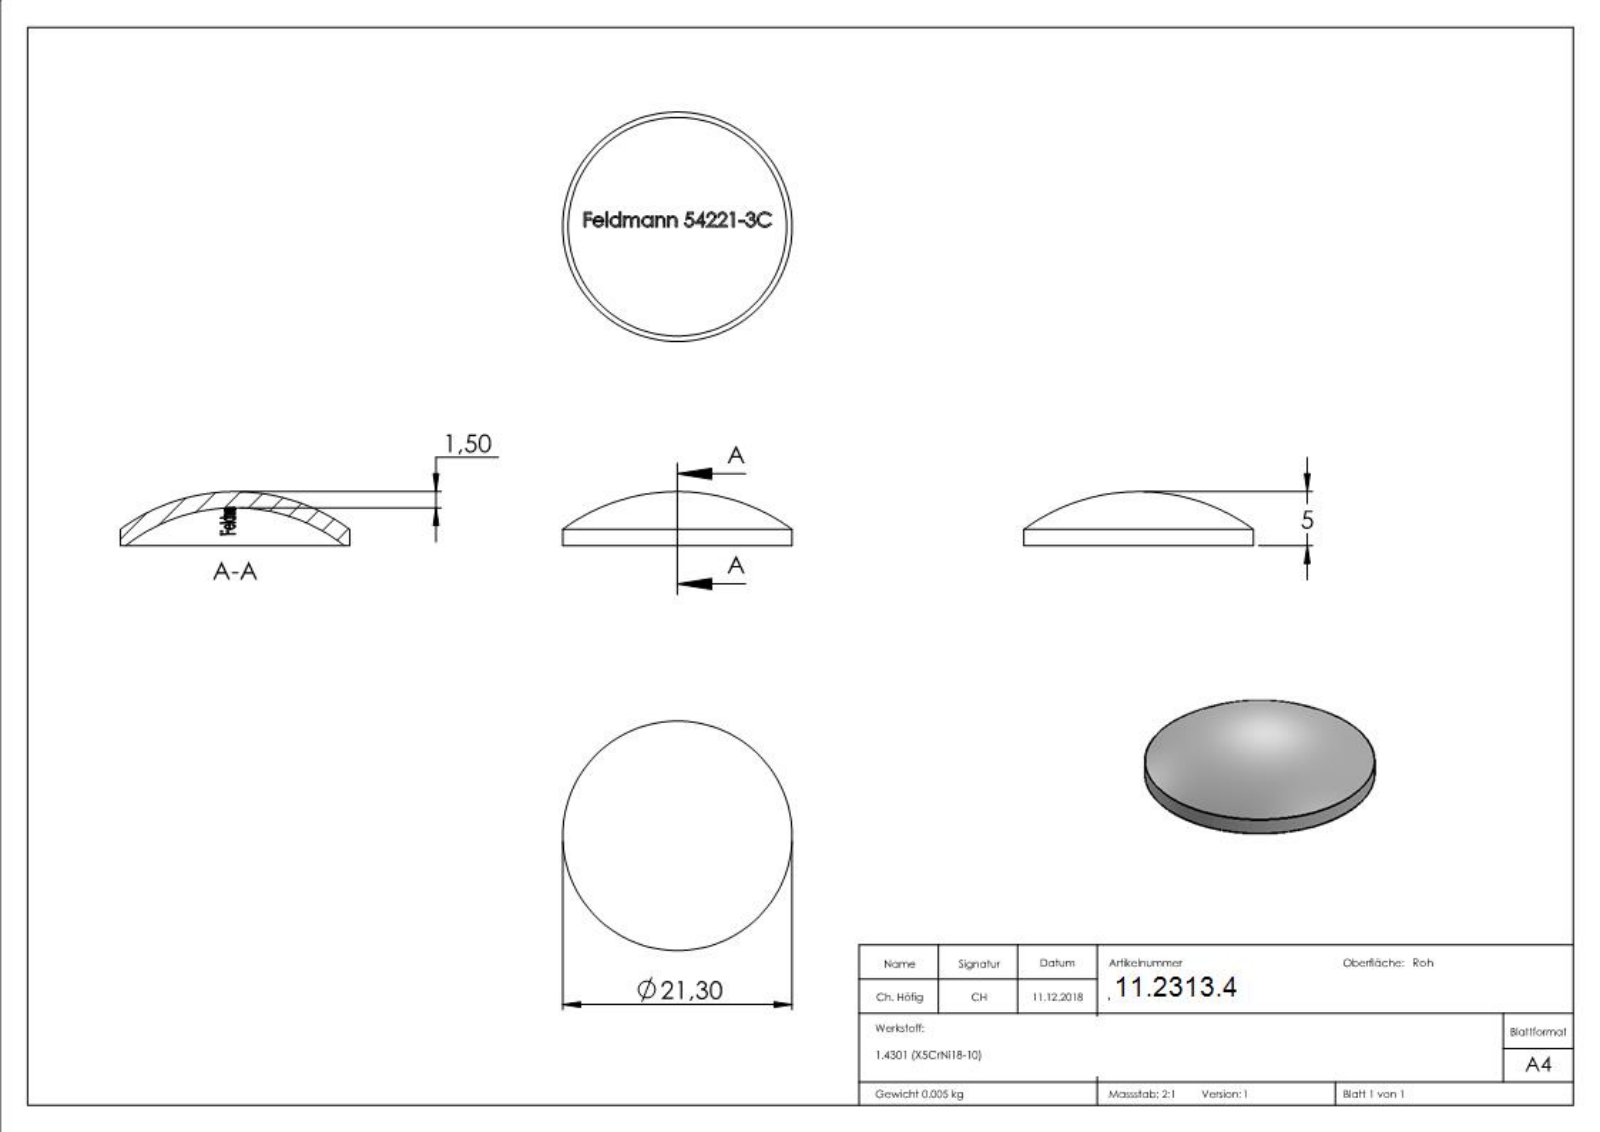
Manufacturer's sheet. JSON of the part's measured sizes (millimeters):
{"part_name": "54221-3C", "step_written_by": "SolidWorks 2015 (CONFIG_CONTROL_DESIGN)", "units": "millimeters", "bodies": {"solids": 1, "faces": 230, "planar": 101, "cylindrical": 2, "other": 127}, "overall_size": [21.3, 21.3, 5], "volume_mm3": 592, "surface_area_mm2": 899, "round_bosses_or_shafts": [[21.3, 1]], "face_to_face_distances": [0.39, 2.97, 0.44, 11.75, 2.02, 13.77, 1.25, 8.92, 2.83, 10.5]}
